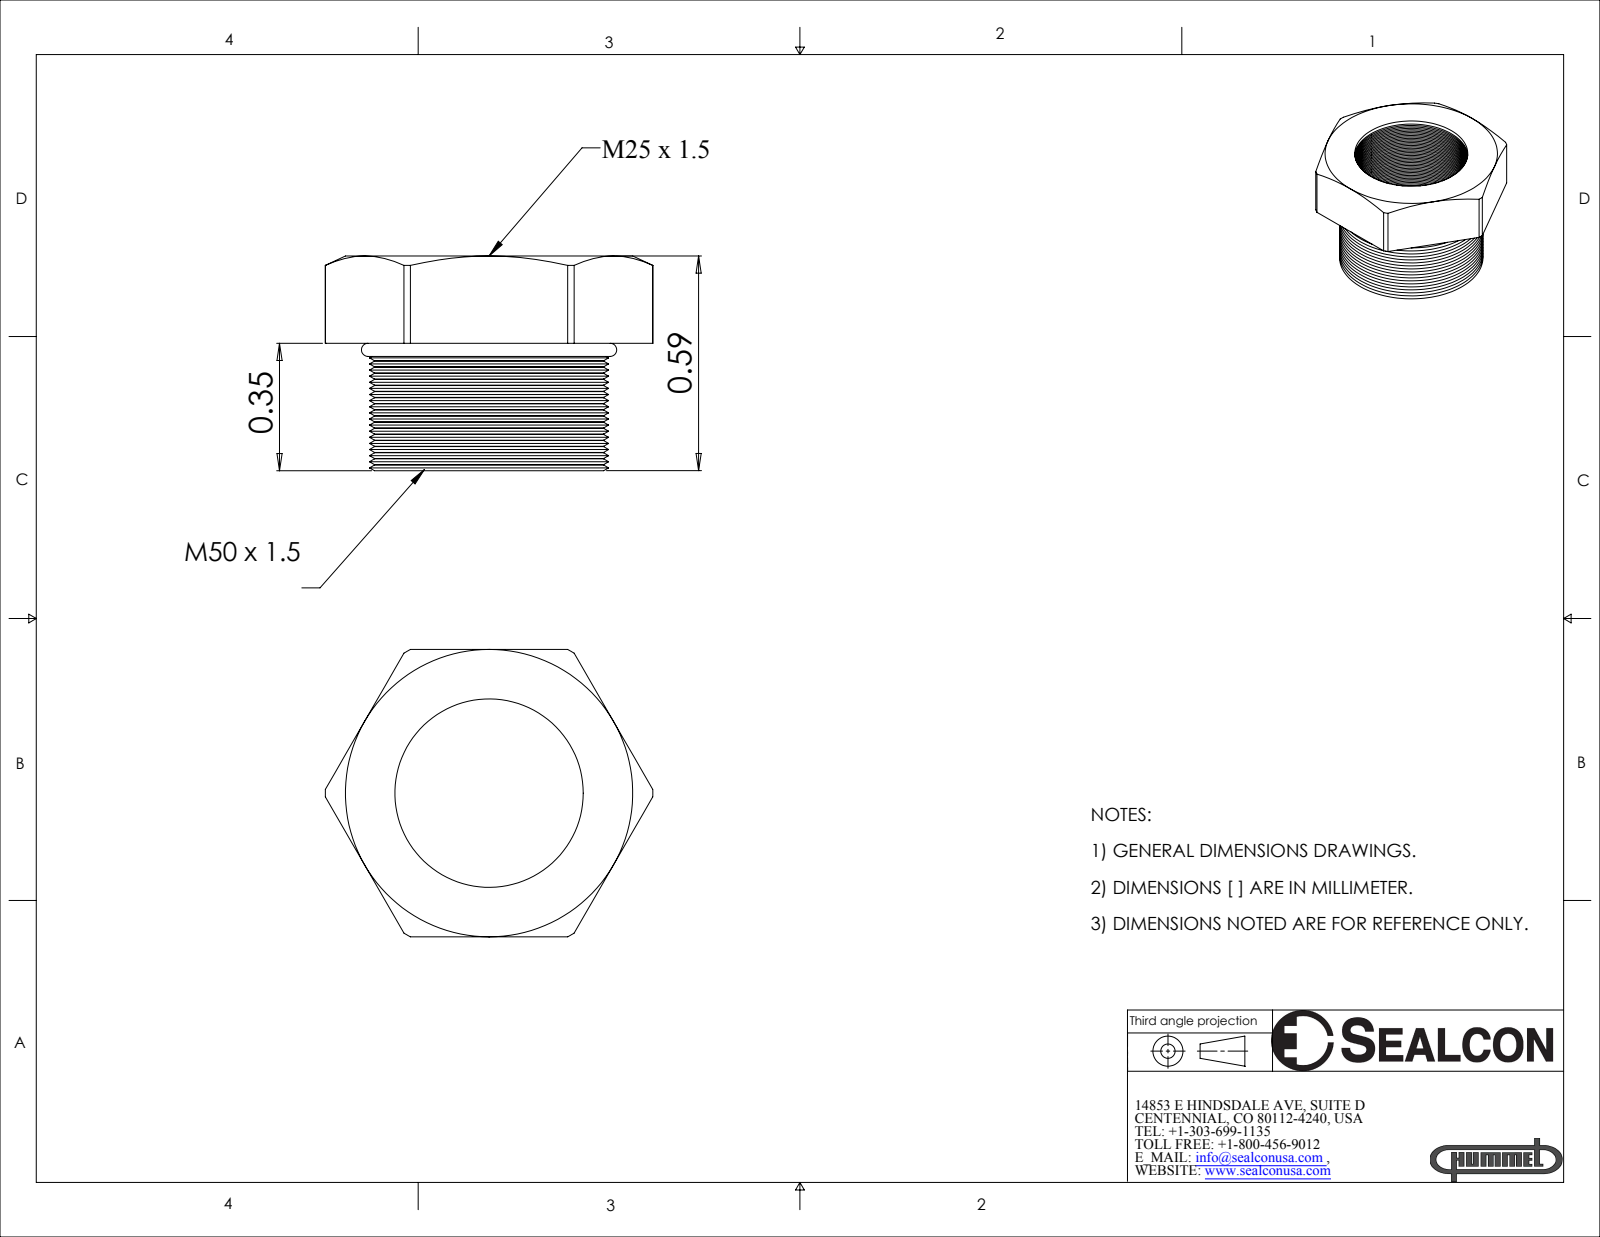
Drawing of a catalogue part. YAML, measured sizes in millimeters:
part_name: "RM-5025-SS-B"
step_written_by: "SolidWorks 2008 (CONFIG_CONTROL_DESIGN)"
units: millimeters
bodies: {solids: 2, faces: 361, planar: 9, cylindrical: 121, other: 231}
overall_size: [22.9, 20.1, 15]
volume: 1930
surface_area: 3090
round_holes:
  - {diameter: 13.2, count: 1}
round_bosses_or_shafts:
  - {diameter: 16, count: 1}
partial_cylinders:
  - {radius: 11.4, count: 1}
face_to_face_distances: [20.1, 6.1, 8.9, 15]
